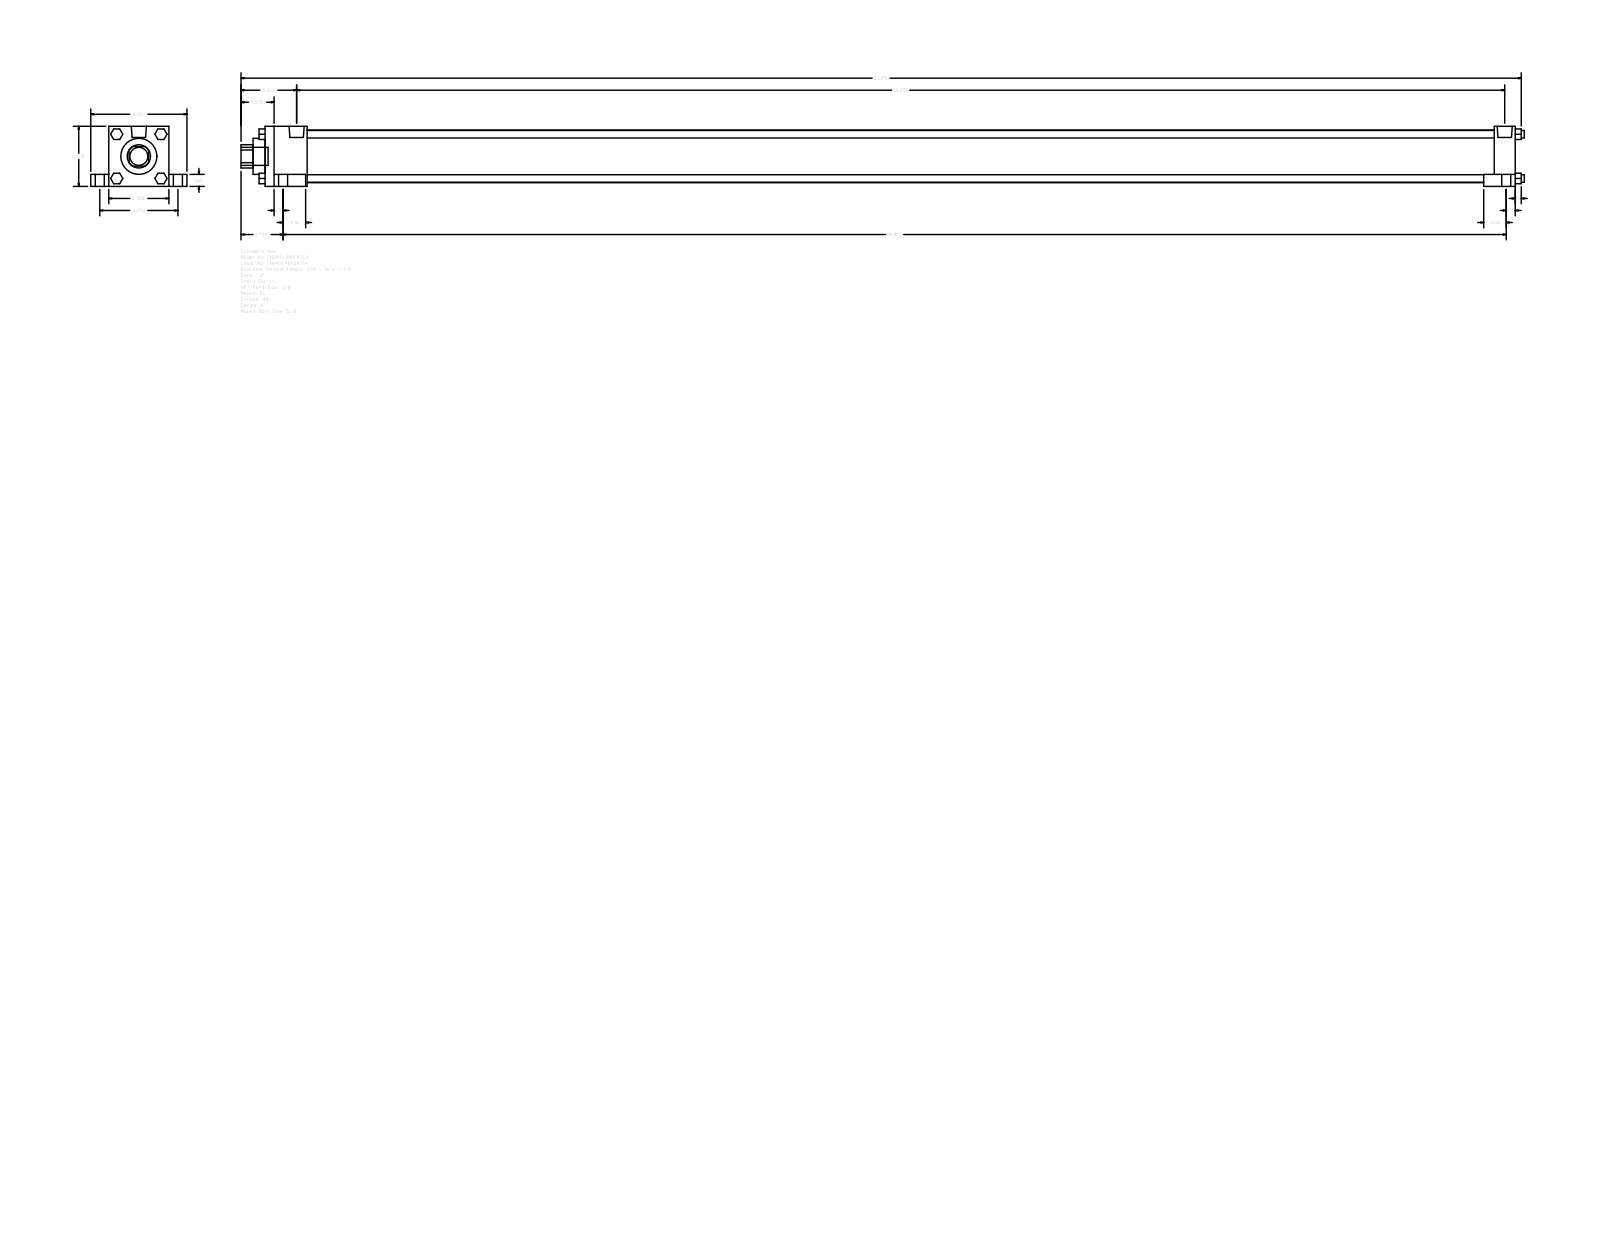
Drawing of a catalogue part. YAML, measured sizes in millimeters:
part_name: "A_SL__0200_1"
step_written_by: "GSSL Pune (CONFIG_CONTROL_DESIGN)"
units: millimeters
bodies: {solids: 0, faces: 148, planar: 112, cylindrical: 36, other: 0}
overall_size: [1355.72, 101.6, 63.5]
round_holes:
  - {diameter: 25.4, count: 1}
  - {diameter: 38.1, count: 1}
  - {diameter: 55.63, count: 1}
round_bosses_or_shafts:
  - {diameter: 15.88, count: 4}
  - {diameter: 9.53, count: 4}
  - {diameter: 7.94, count: 4}
  - {diameter: 5.56, count: 4}
  - {diameter: 15.93, count: 2}
  - {diameter: 19.05, count: 1}
partial_cylinders:
  - {radius: 12.29, count: 1}
face_to_face_distances: [63.5, 1320.8, 12.7, 50.8, 19.05, 82.55, 9.52, 44.45, 1276.35, 1298.57]
